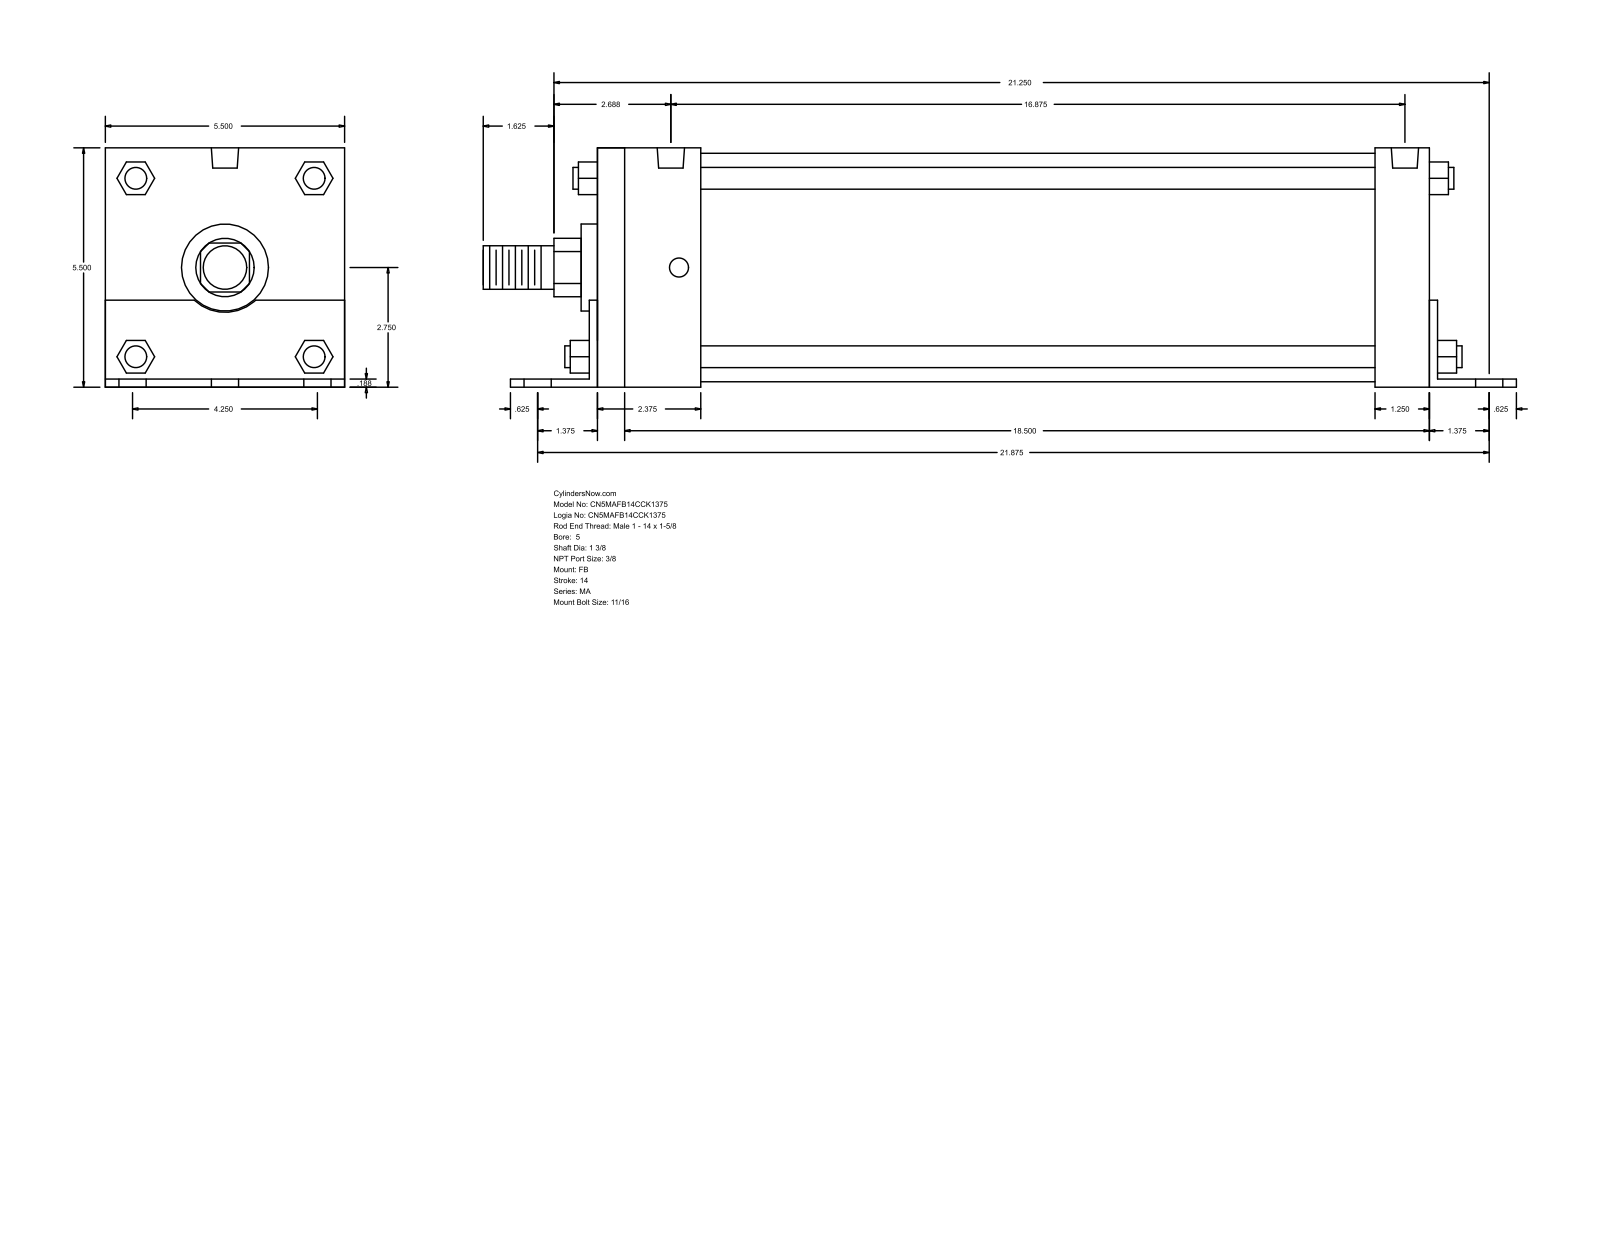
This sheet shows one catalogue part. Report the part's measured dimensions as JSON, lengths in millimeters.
{"part_name": "MA_FB__0500_1.375", "step_written_by": "GSSL Pune (CONFIG_CONTROL_DESIGN)", "units": "millimeters", "bodies": {"solids": 0, "faces": 140, "planar": 105, "cylindrical": 35, "other": 0}, "overall_size": [603.25, 139.75, 139.7], "round_holes": [[17.46, 6], [11.11, 4], [15.93, 2]], "round_bosses_or_shafts": [[12.7, 4], [133.35, 1], [50.8, 1], [34.92, 1], [25.4, 1]], "partial_cylinders_radius": [[17.06, 1], [26.16, 1]], "face_to_face_distances": [139.7, 4.76, 139.75, 490.54, 4.71, 134.99, 485.78, 495.3, 31.75, 36.51], "hole_center_spacings": [53.98, 558.25, 555.63, 4.77, 73.04, 76.34, 94.68, 98.64]}
